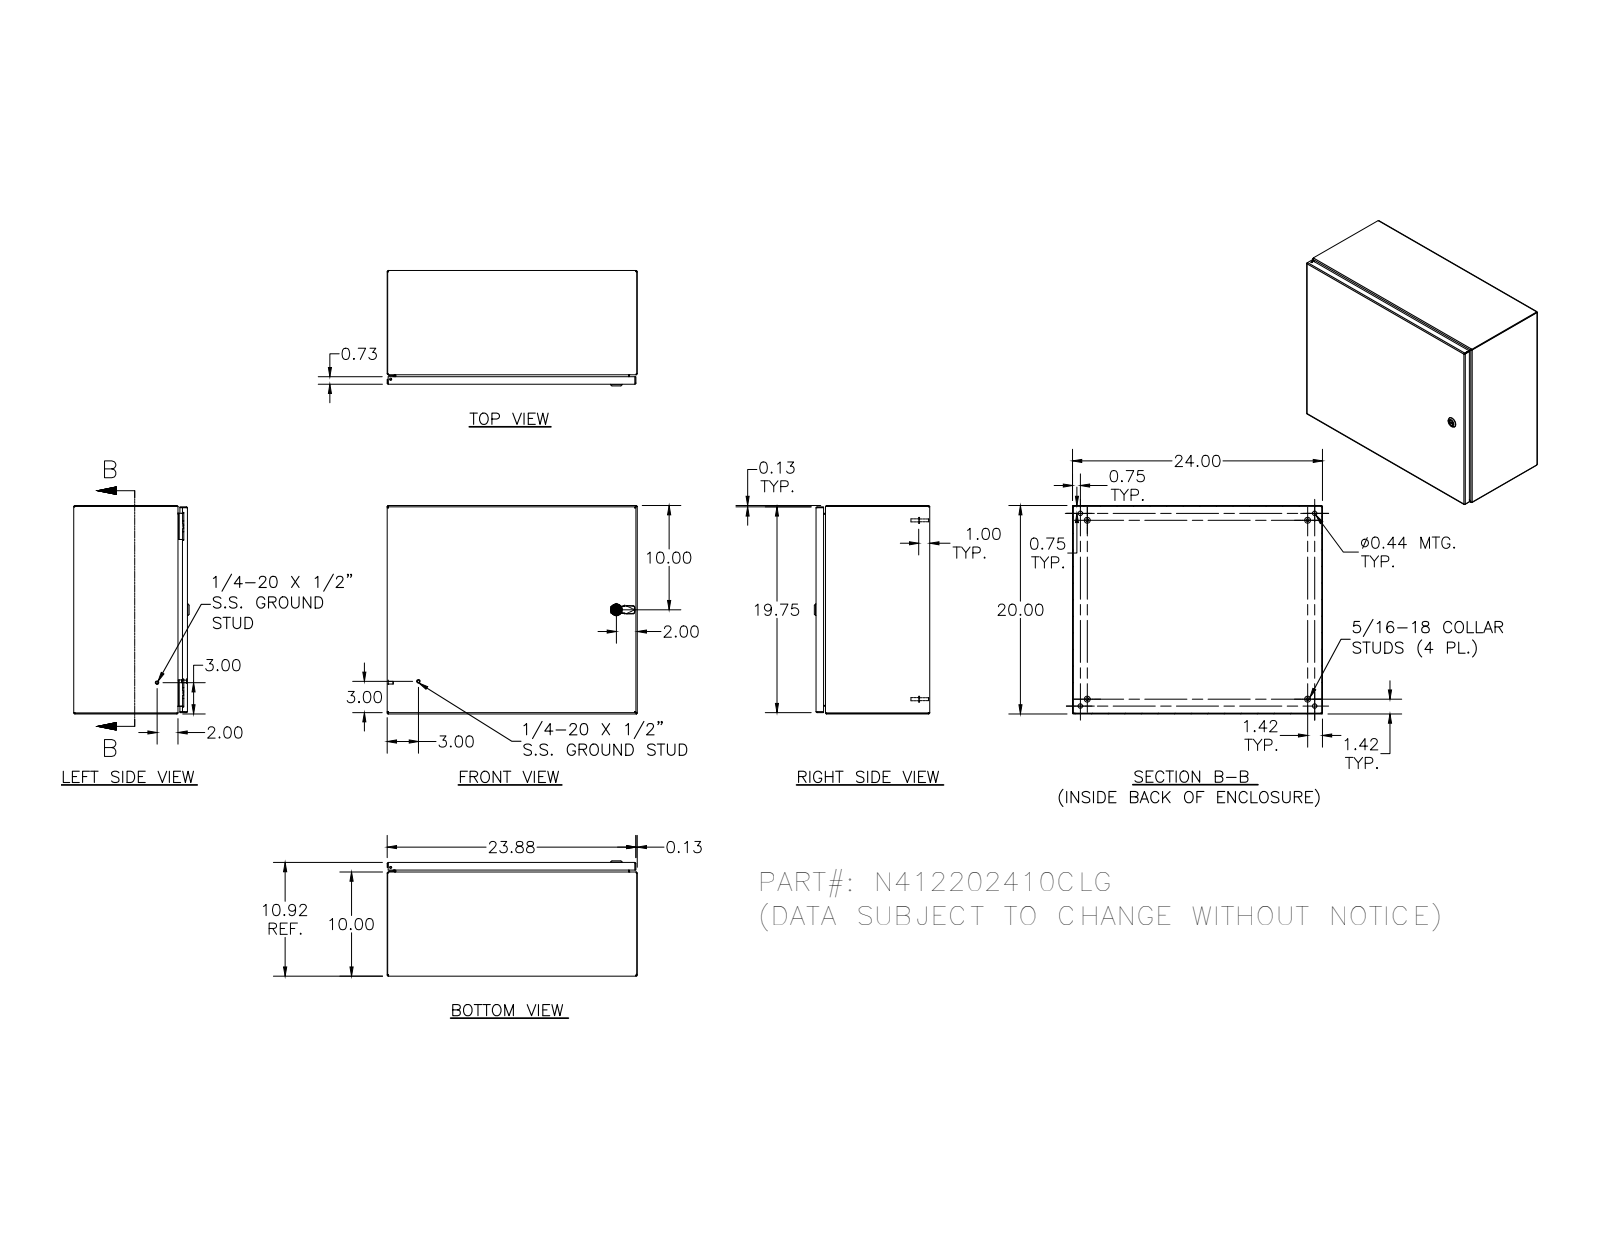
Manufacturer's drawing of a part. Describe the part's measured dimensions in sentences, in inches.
The part is named "N412202410CLG". Its 3-D file was written by "SolidWorks 2018 (AUTOMOTIVE_DESIGN)". It is 33 solids with 1449 faces: 530 planar, 547 cylindrical and 372 other. Overall it measures 24 by 20 by 11.075 inches. Its volume is 149.2 cubic inches and its surface area 4 054 square inches. Round holes: 5 of diameter 0.188, 4 of diameter 0.093, 4 of diameter 0.152, 4 of diameter 0.167, 4 of diameter 0.172, 4 of diameter 0.437, 2 of diameter 0.156, 1 of diameter 0.187, 1 of diameter 0.197, 1 of diameter 0.315, 1 of diameter 0.394, 1 of diameter 0.402. Round bosses or shafts: 10 of diameter 0.25, 4 of diameter 0.563, 4 of diameter 0.36, 4 of diameter 0.32, 4 of diameter 0.3, 4 of diameter 0.275, 4 of diameter 0.256, 4 of diameter 0.164. Partial cylindrical surfaces (rounded edges, fillets, slot ends): 30 of radius 0.012, 30 of radius 0.031, 26 of radius 0.05, 20 of radius 0.105, 18 of radius 0.016, 16 of radius 0.125, 13 of radius 0.02, 8 of radius 0.032. The main face-to-face distances are 0.074, 10.843, 10.769, 10.917, 0.074, 19.926, 19.852, 20, 19.926, 23.926. The hole center spacings are 16, 0.66, 0.656, 1.307, 1.965, 15.34, 15.996, 16.656.
